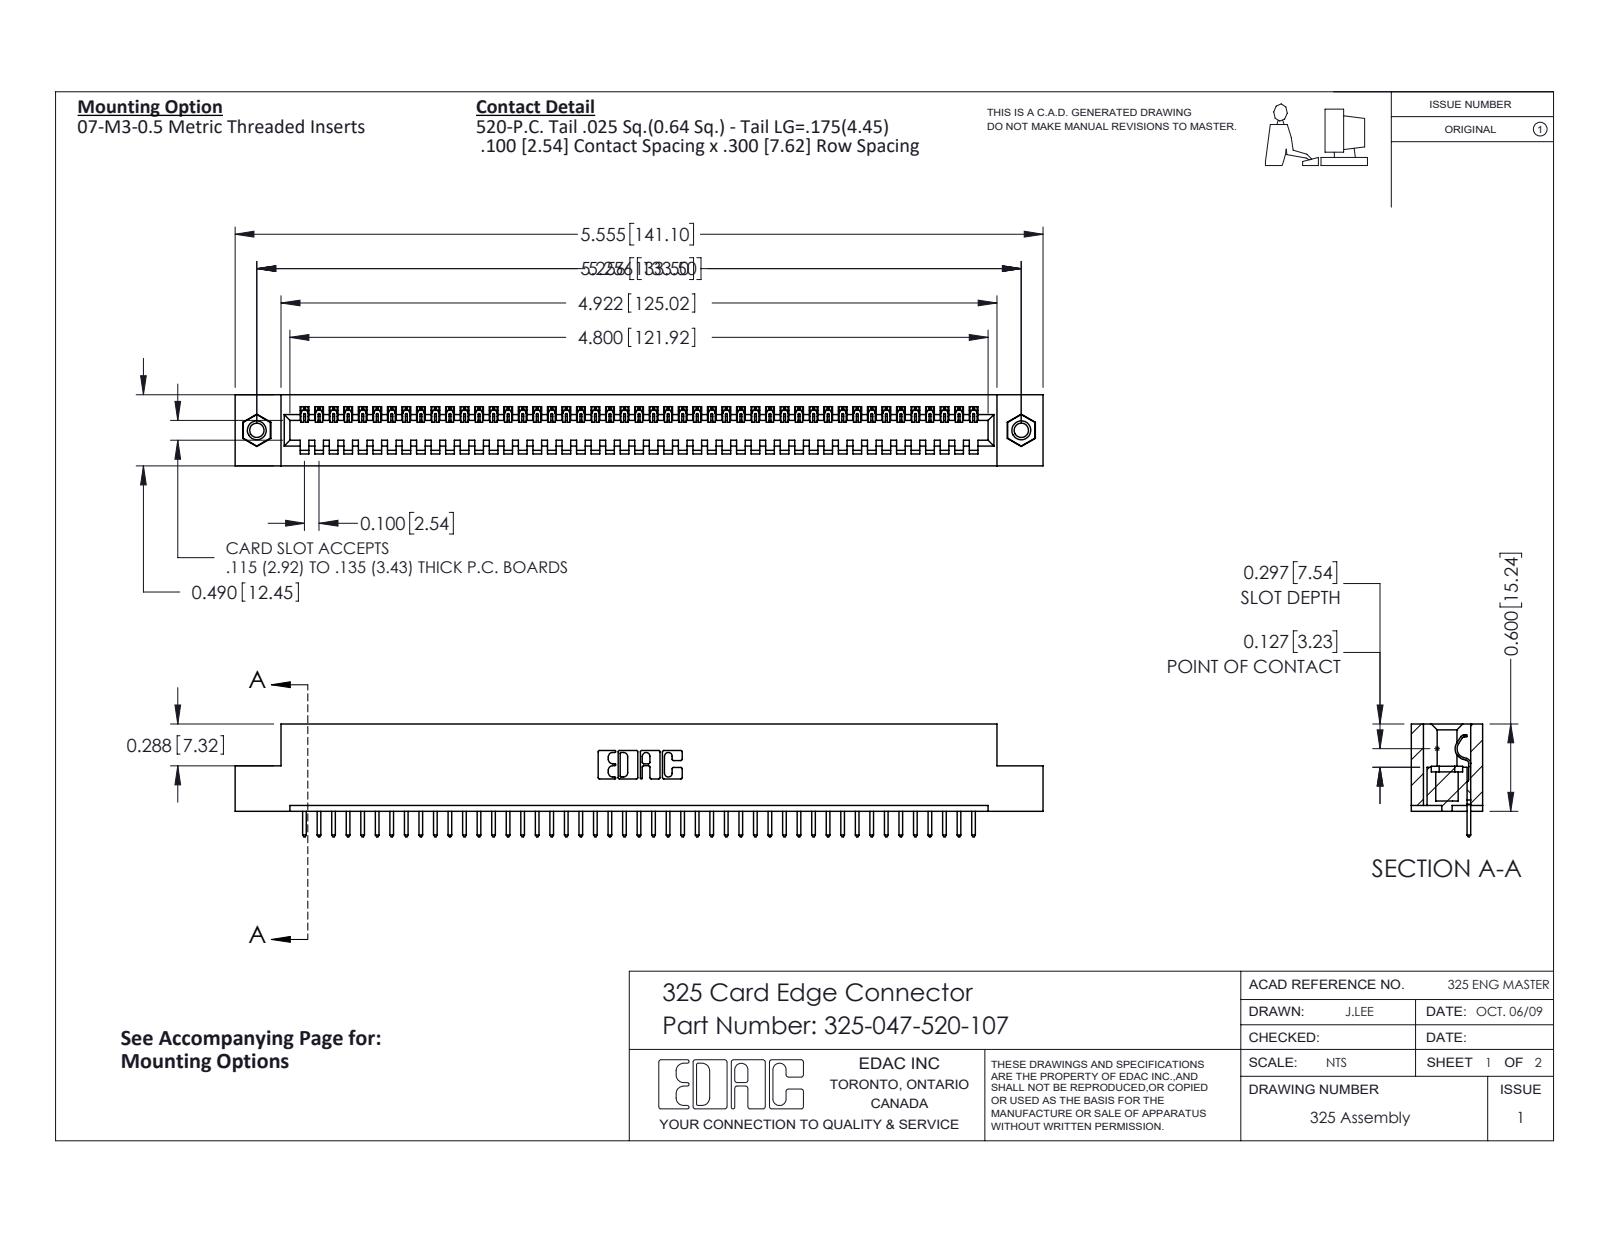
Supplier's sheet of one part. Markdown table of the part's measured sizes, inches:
| quantity | value |
| --- | --- |
| part name | 345-250-001_345-250-005-103; 325-292-001_325-293-120; 325 Part_TI; 325-047-520-107 |
| STEP written by | SolidWorks 2016 (CONFIG_CONTROL_DESIGN) |
| units | inches |
| bodies | 50 solids, 2900 faces (2076 planar, 808 cylindrical, 16 other) |
| overall size | 5.555 × 0.775 × 0.49 |
| volume | 1.087 in³ |
| surface area | 29.58 in² |
| round holes (diameter × count) | 0.098 × 2, 0.125 × 2, 0.16 × 2 |
| round bosses / shafts (diameter × count) | 0.155 × 2 |
| partial cylindrical surfaces (radius × count) | 0.006 × 94, 0.01 × 94, 0.01 × 22, 0.007 × 6, 0.031 × 6, 0.026 × 3, 0.014 × 1, 0.022 × 1 |
| main face-to-face distances | 0.083, 0.407, 0.49, 0.3, 0.107, 0.383, 0.025, 0.325, 0.56, 0.263 |
| hole center spacings | 5.256 |
